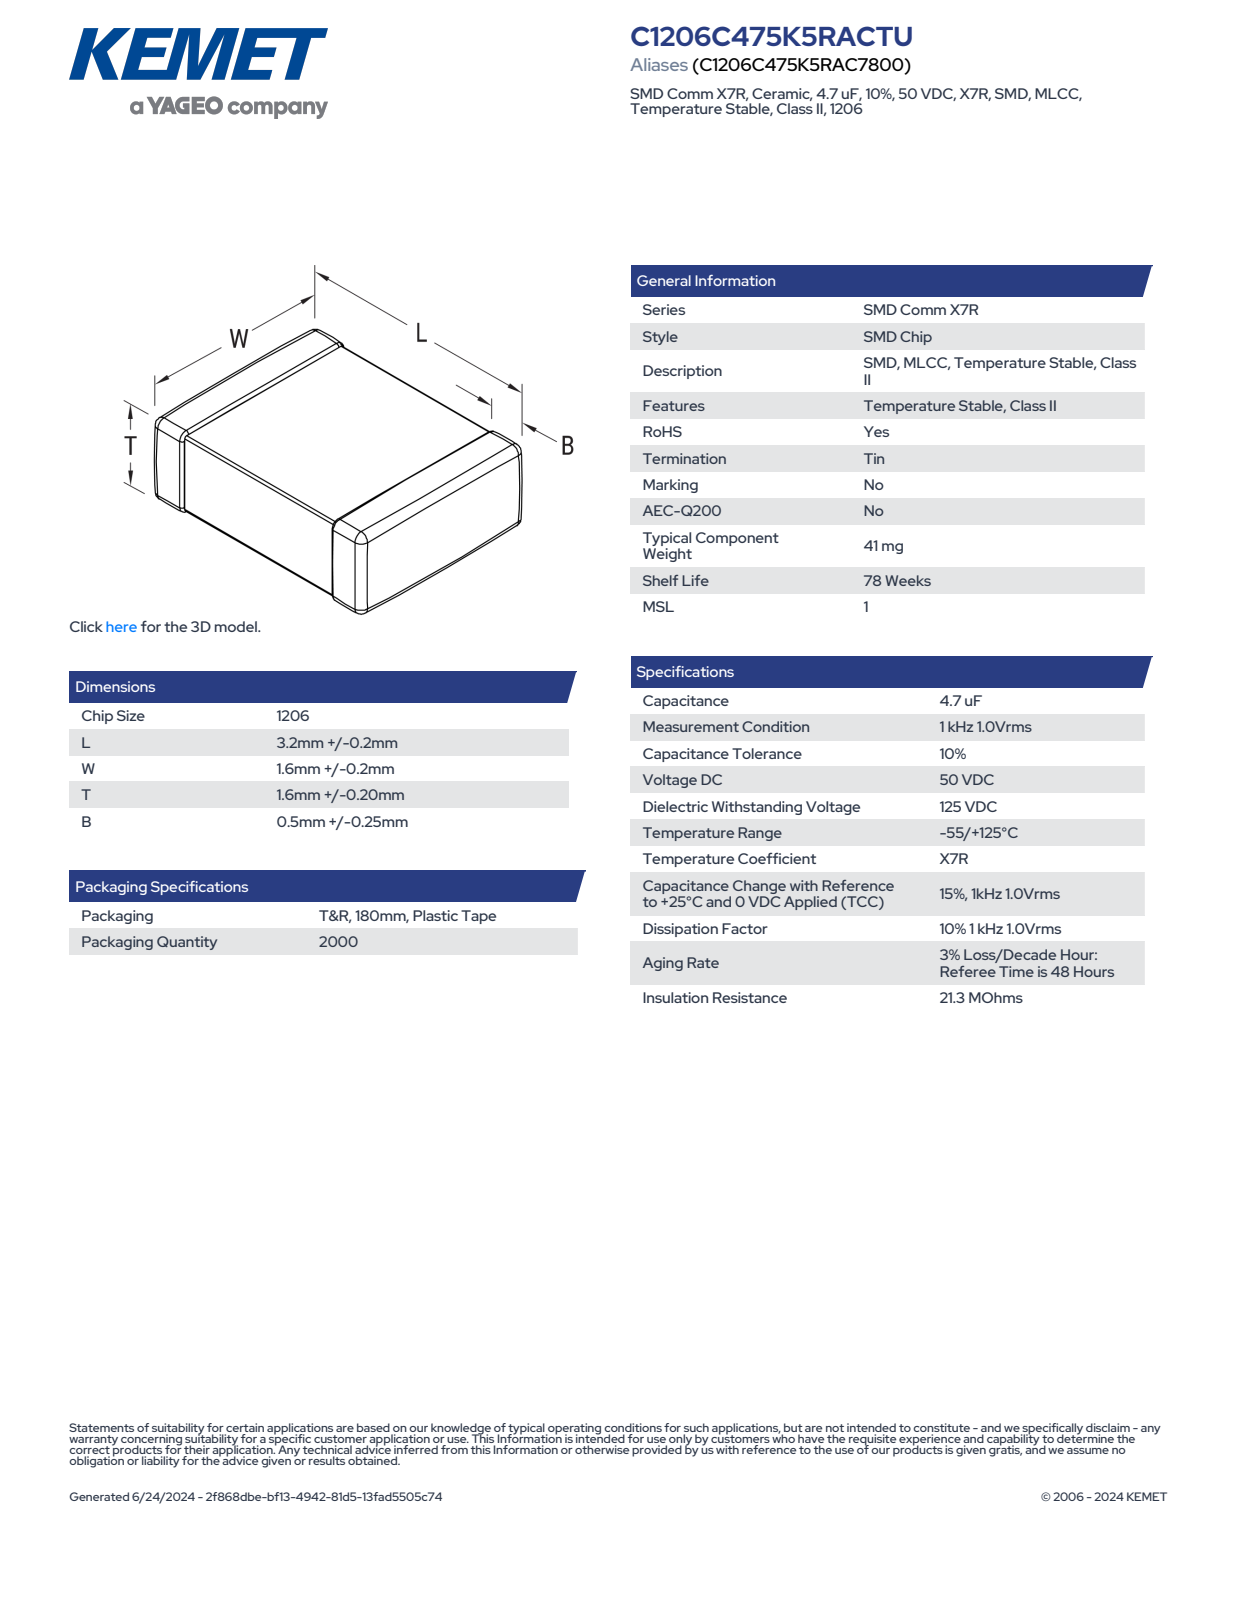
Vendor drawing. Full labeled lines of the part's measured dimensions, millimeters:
Part name (STEP PRODUCT): CCS_CCSTD_1206_L3.4W1.8T1.8B0.5
STEP written by: SolidWorks 2021 (AUTOMOTIVE_DESIGN)
Units: millimetres
Bodies: 4 solids, 121 faces (71 planar, 34 cylindrical, 16 other)
Overall size (bounding box): 2.2 × 1.45 × 0.9
Volume: 3 mm³ · Surface area: 13 mm²
Main face-to-face distances: 0.87, 0.9, 2.2, 1.45, 1.42, 0.84, 1.39, 0.97, 1.23, 1.19
